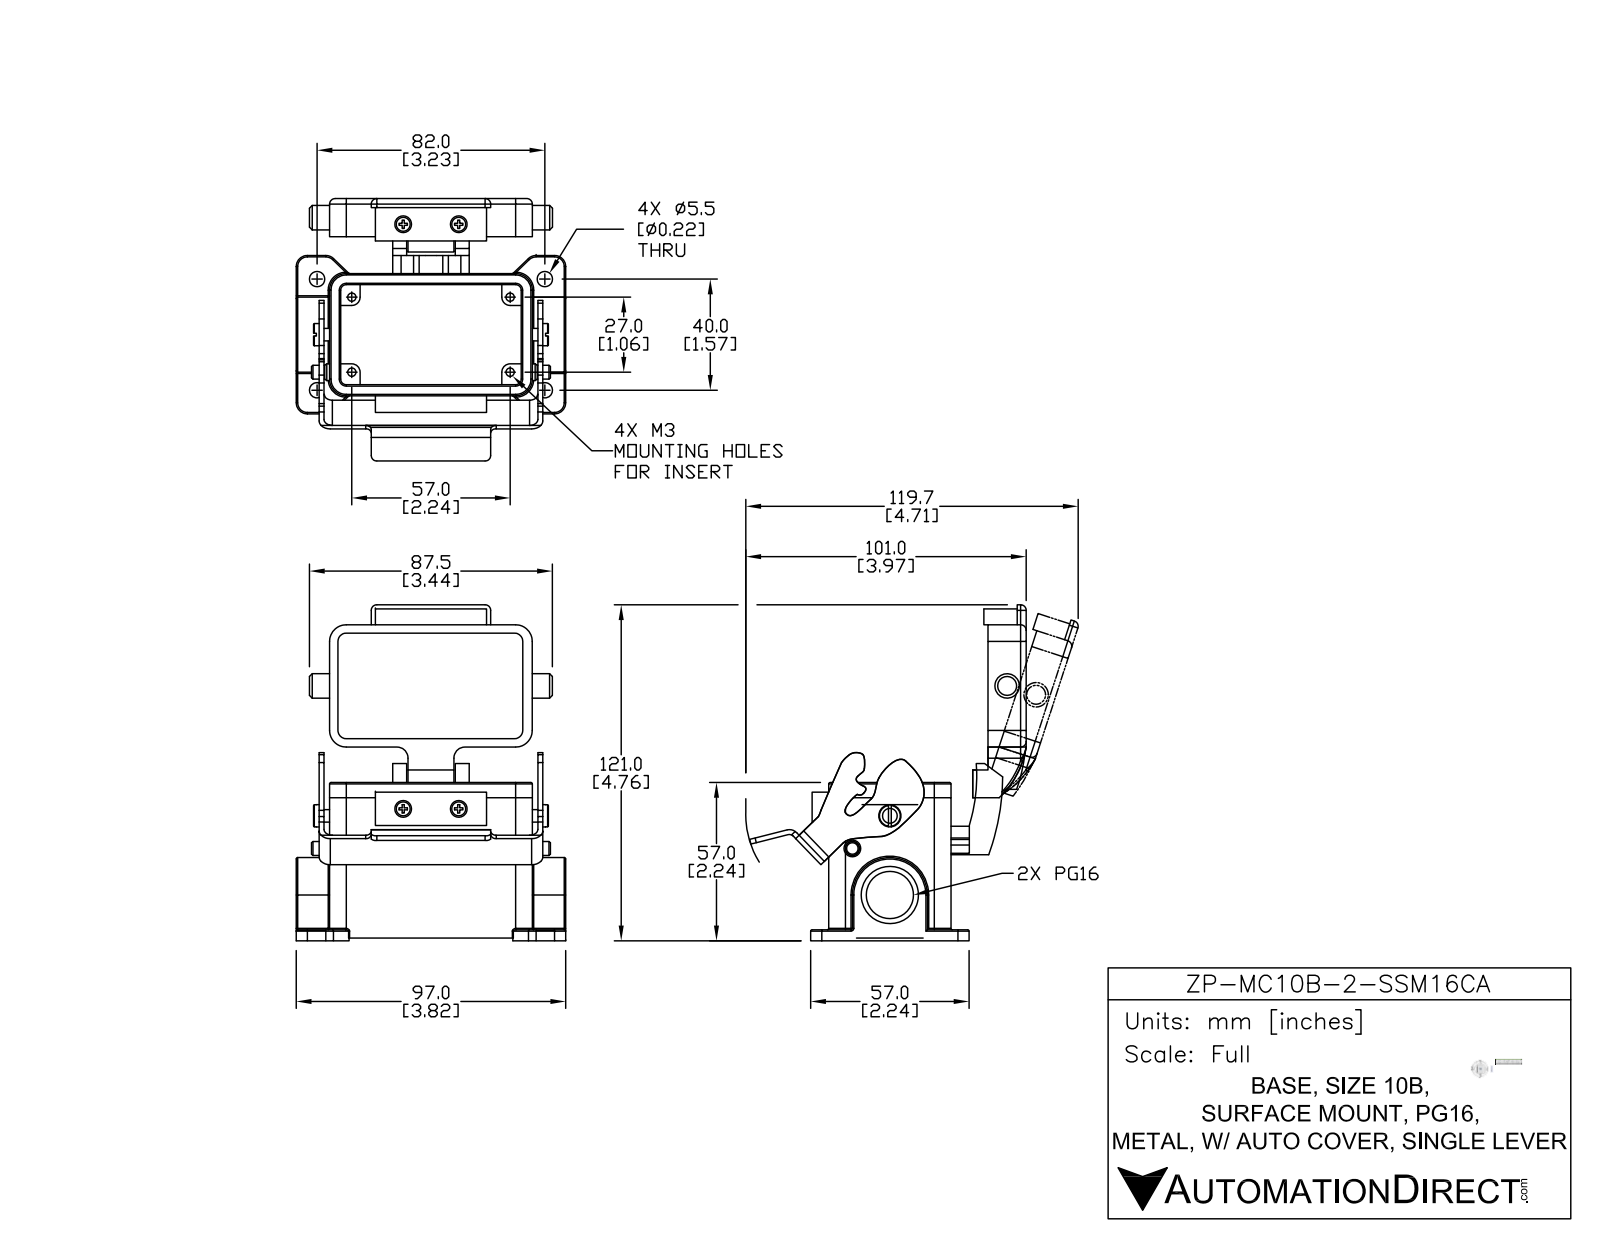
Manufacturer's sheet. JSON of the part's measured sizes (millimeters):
{"part_name": "ZP-MC10B-2-SSM16CA", "step_written_by": "SolidWorks 2014 (AUTOMOTIVE_DESIGN)", "units": "millimeters", "bodies": {"solids": 11, "faces": 534, "planar": 228, "cylindrical": 176, "other": 130}, "overall_size": [121.25, 97, 94.45], "volume_mm3": 110912, "surface_area_mm2": 66316, "round_holes": [[3, 4], [5.5, 4], [4.5, 1], [5.32, 1], [17, 1], [20.6, 1]], "round_bosses_or_shafts": [[5, 5], [8, 2], [8.8, 1], [6, 1]], "partial_cylinders_radius": [[0.5, 32], [2, 23], [3, 12], [4, 12], [6, 8], [3.75, 1], [4.25, 1], [13.5, 1]], "face_to_face_distances": [4, 40, 1.75, 5, 44, 1, 26.98, 70.98, 12, 3], "hole_center_spacings": [13.87, 35.67, 70.05, 77.38, 27, 40, 57.5, 63.52]}
